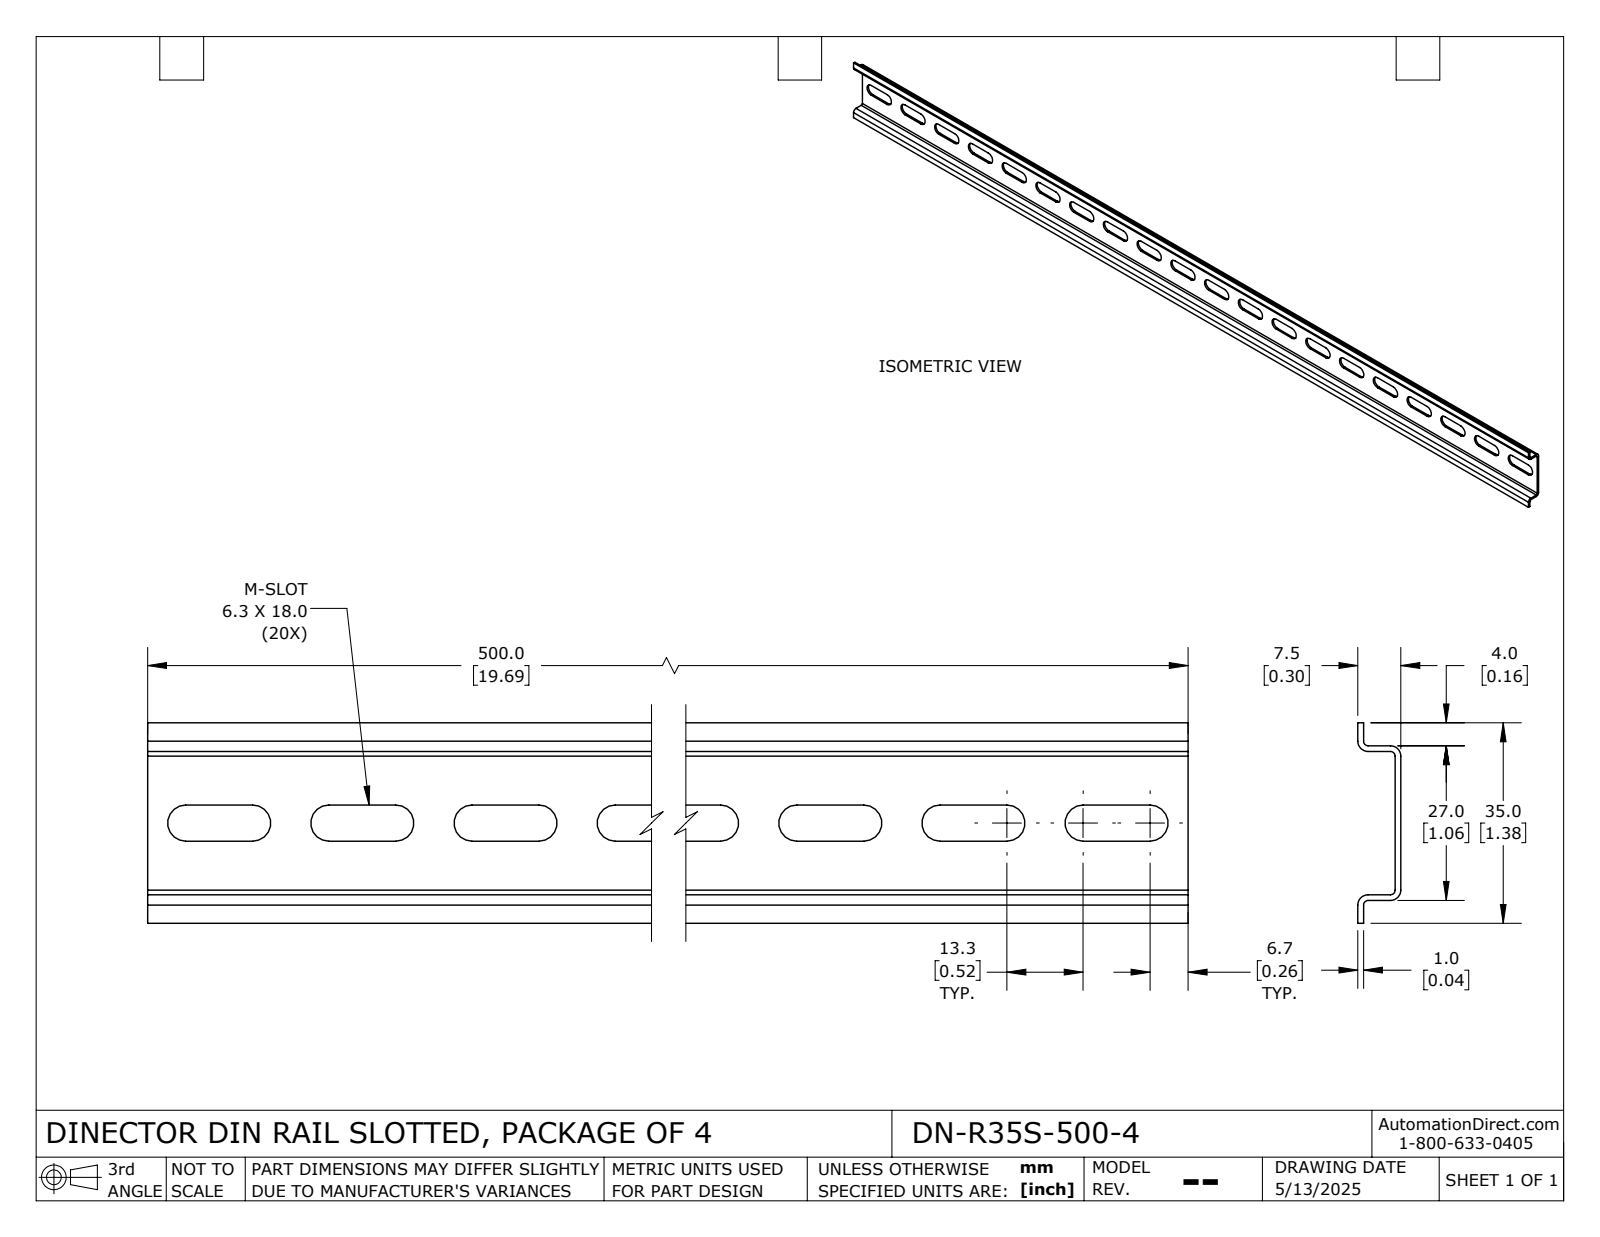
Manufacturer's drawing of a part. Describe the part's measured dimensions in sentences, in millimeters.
The part is named "DN-R35S-500-4_Default". Its 3-D file was written by "SolidWorks 2024 (CONFIG_CONTROL_DESIGN)". It is 1 solid with 102 faces: 54 planar, 48 cylindrical and 0 other. Overall it measures 500 by 35 by 7.5 millimeters. Its volume is 20 786 cubic millimeters and its surface area 43 528 square millimeters. Partial cylindrical surfaces (rounded edges, fillets, slot ends): 40 of radius 3.15, 4 of radius 0.8, 4 of radius 1.8. The main face-to-face distances are 1, 6.5, 26, 7.5, 5.5, 27, 25, 4, 5, 30.
